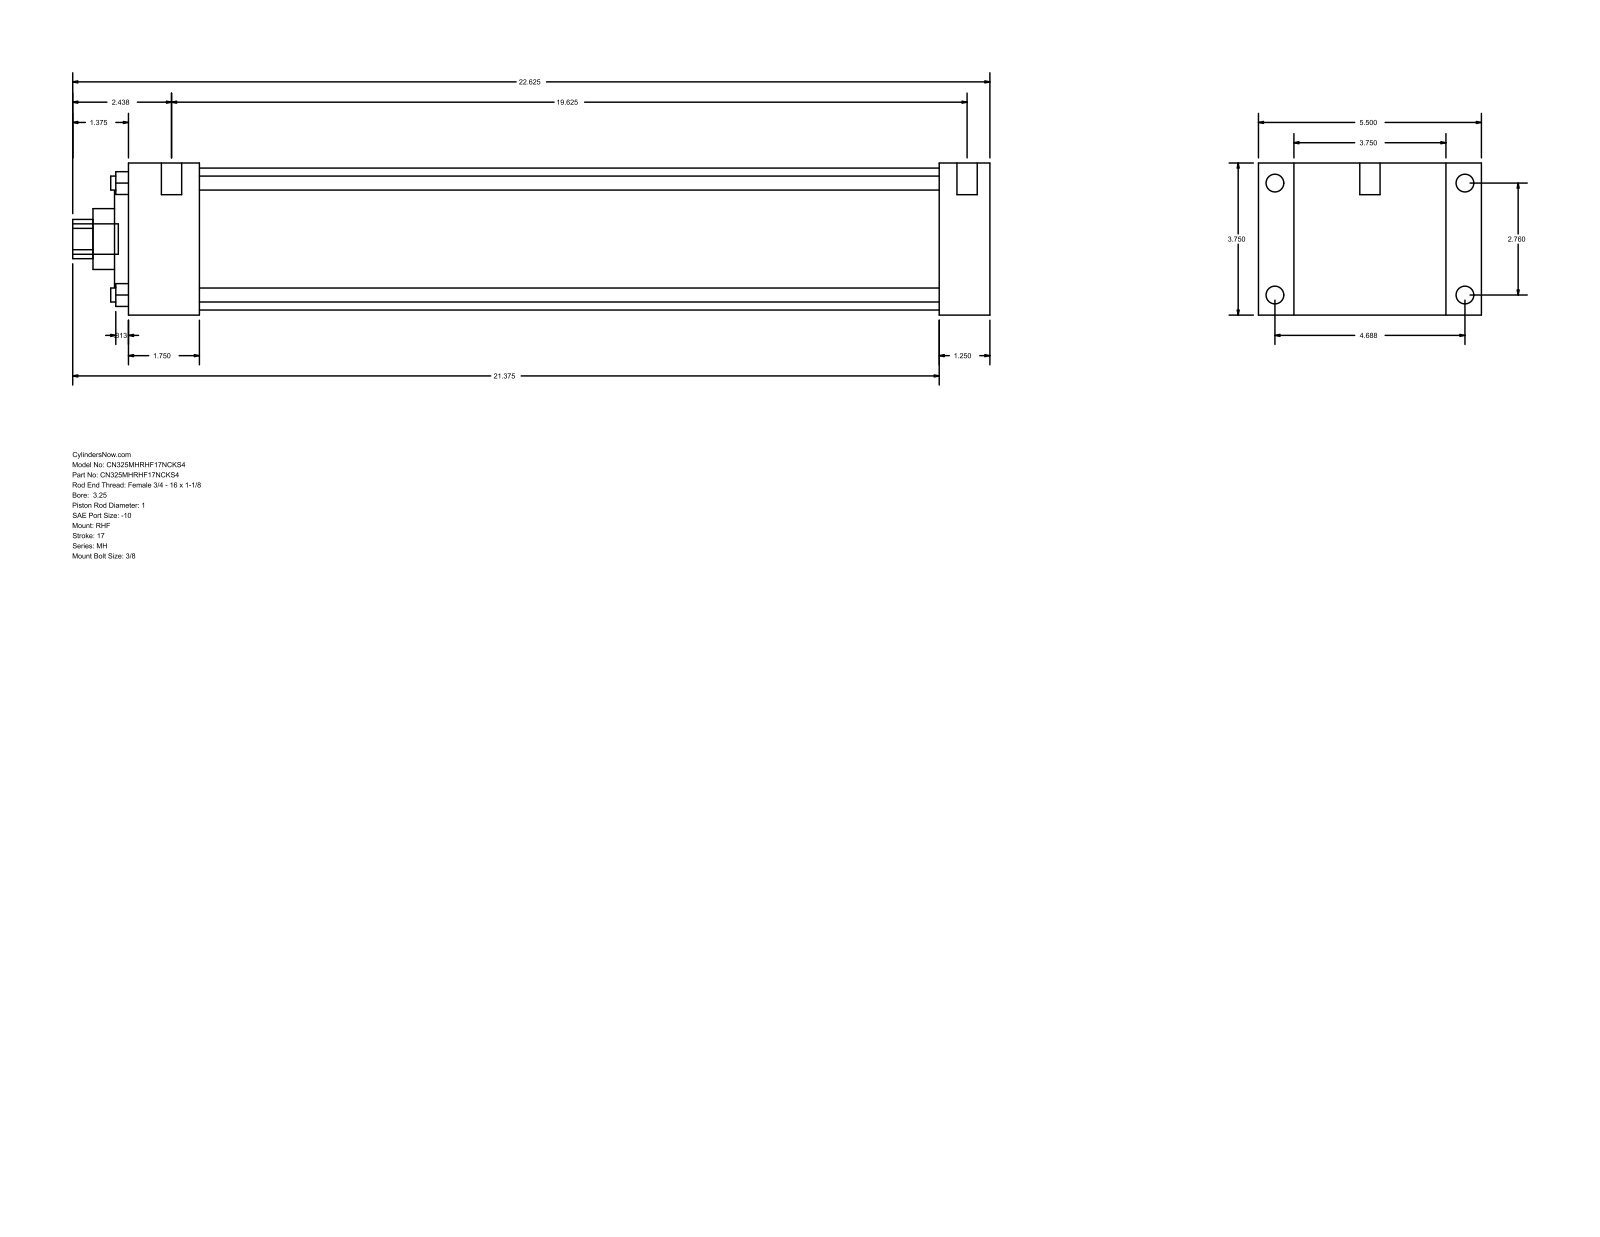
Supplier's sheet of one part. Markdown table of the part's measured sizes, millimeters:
| quantity | value |
| --- | --- |
| part name | MH_RHF__0325_1 |
| STEP written by | GSSL Pune (CONFIG_CONTROL_DESIGN) |
| units | millimeters |
| bodies | 0 solids, 90 faces (61 planar, 29 cylindrical, 0 other) |
| overall size | 574.67 × 139.7 × 95.25 |
| round holes (diameter × count) | 8.76 × 4, 25.4 × 1, 38.1 × 1, 60.33 × 1, 88.9 × 1 |
| round bosses / shafts (diameter × count) | 11.13 × 4, 5.56 × 4, 12.7 × 2, 19.05 × 1 |
| partial cylindrical surfaces (radius × count) | 12.29 × 1 |
| main face-to-face distances | 95.24, 31.75, 22.23, 117.47, 508, 539.75, 139.7, 44.46, 463.54, 495.29 |
| hole center spacings | 49.57, 70.1, 99.14 |
